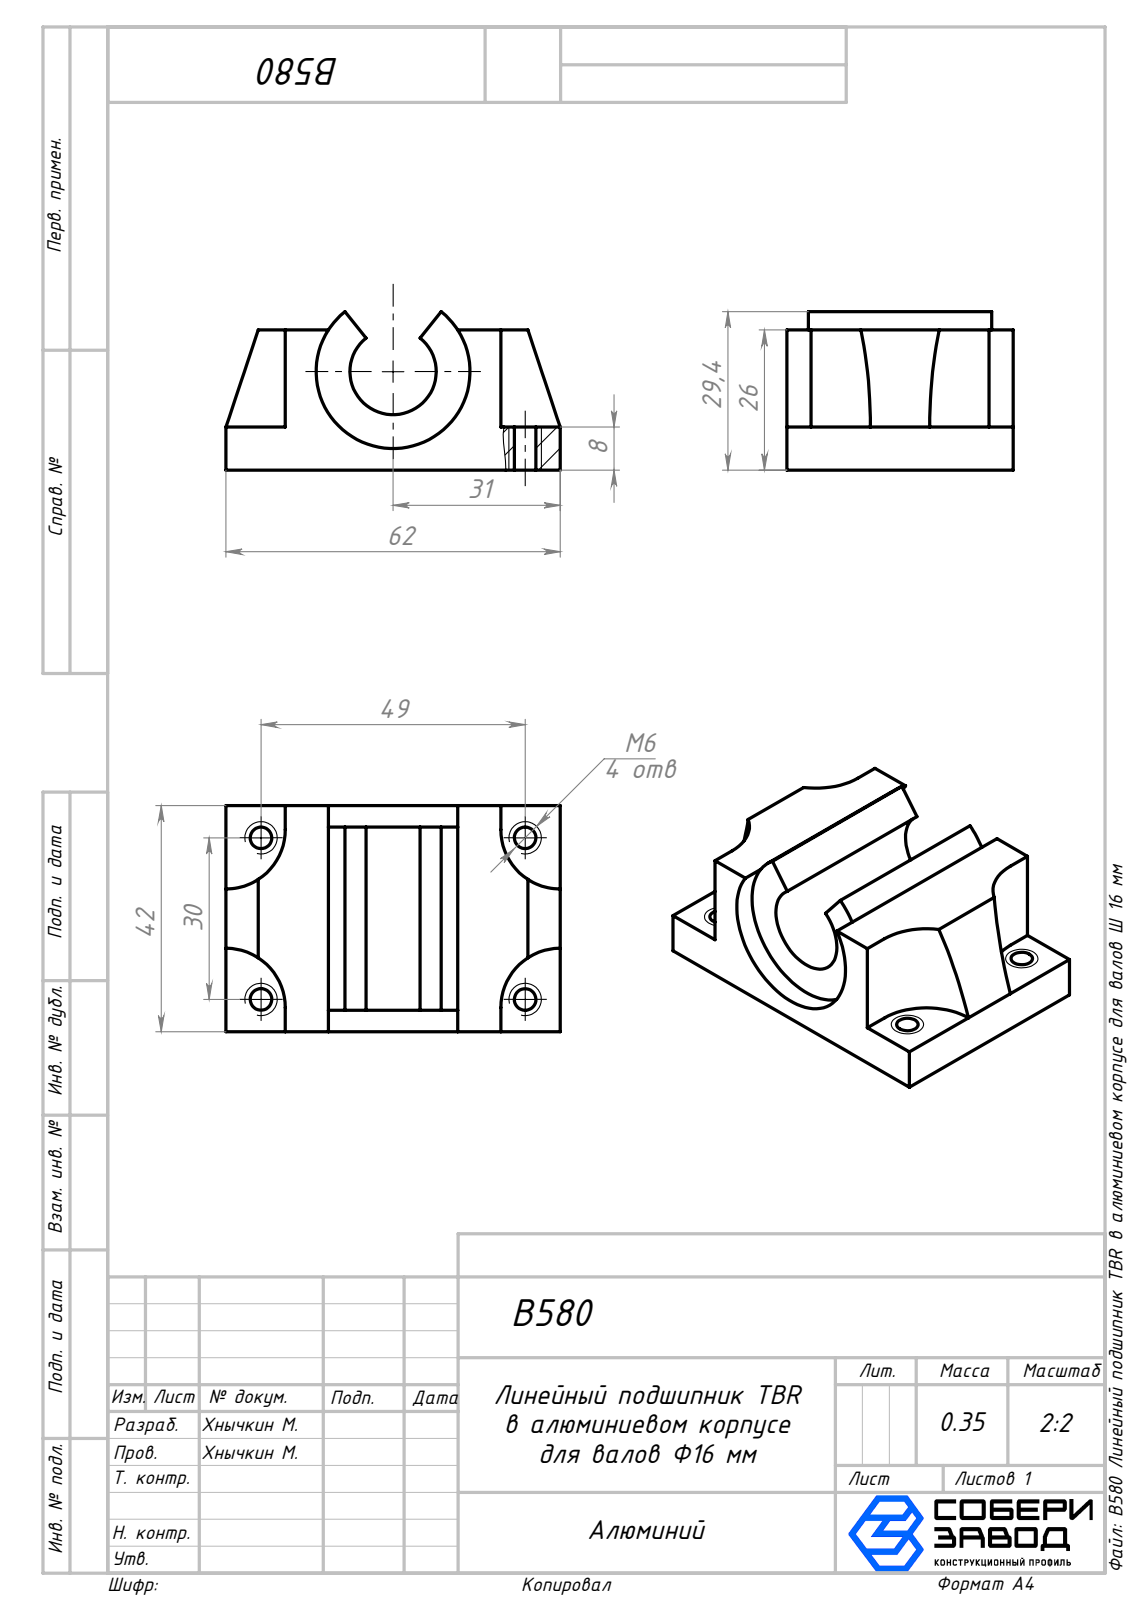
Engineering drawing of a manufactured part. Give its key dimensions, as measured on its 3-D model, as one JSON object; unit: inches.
{"part_name": "B580 Линейный подшипник TBR в алюминиевом корпусе для валов Ø 16 мм", "step_written_by": "SolidWorks 2026 (AUTOMOTIVE_DESIGN)", "units": "inches", "bodies": {"solids": 1, "faces": 44, "planar": 21, "cylindrical": 23, "other": 0}, "overall_size": [2.441, 1.654, 1.158], "volume_in3": 2.754, "surface_area_in2": 17.78, "round_holes": [[0.157, 4]], "partial_cylinders_radius": [[0.433, 4], [0.315, 1], [0.562, 1]], "face_to_face_distances": [1.024, 0.157, 1.496, 1.654, 0.315, 0.709, 1.339, 2.441, 0.433, 2.008], "hole_center_spacings": [1.181, 1.929, 2.262]}
